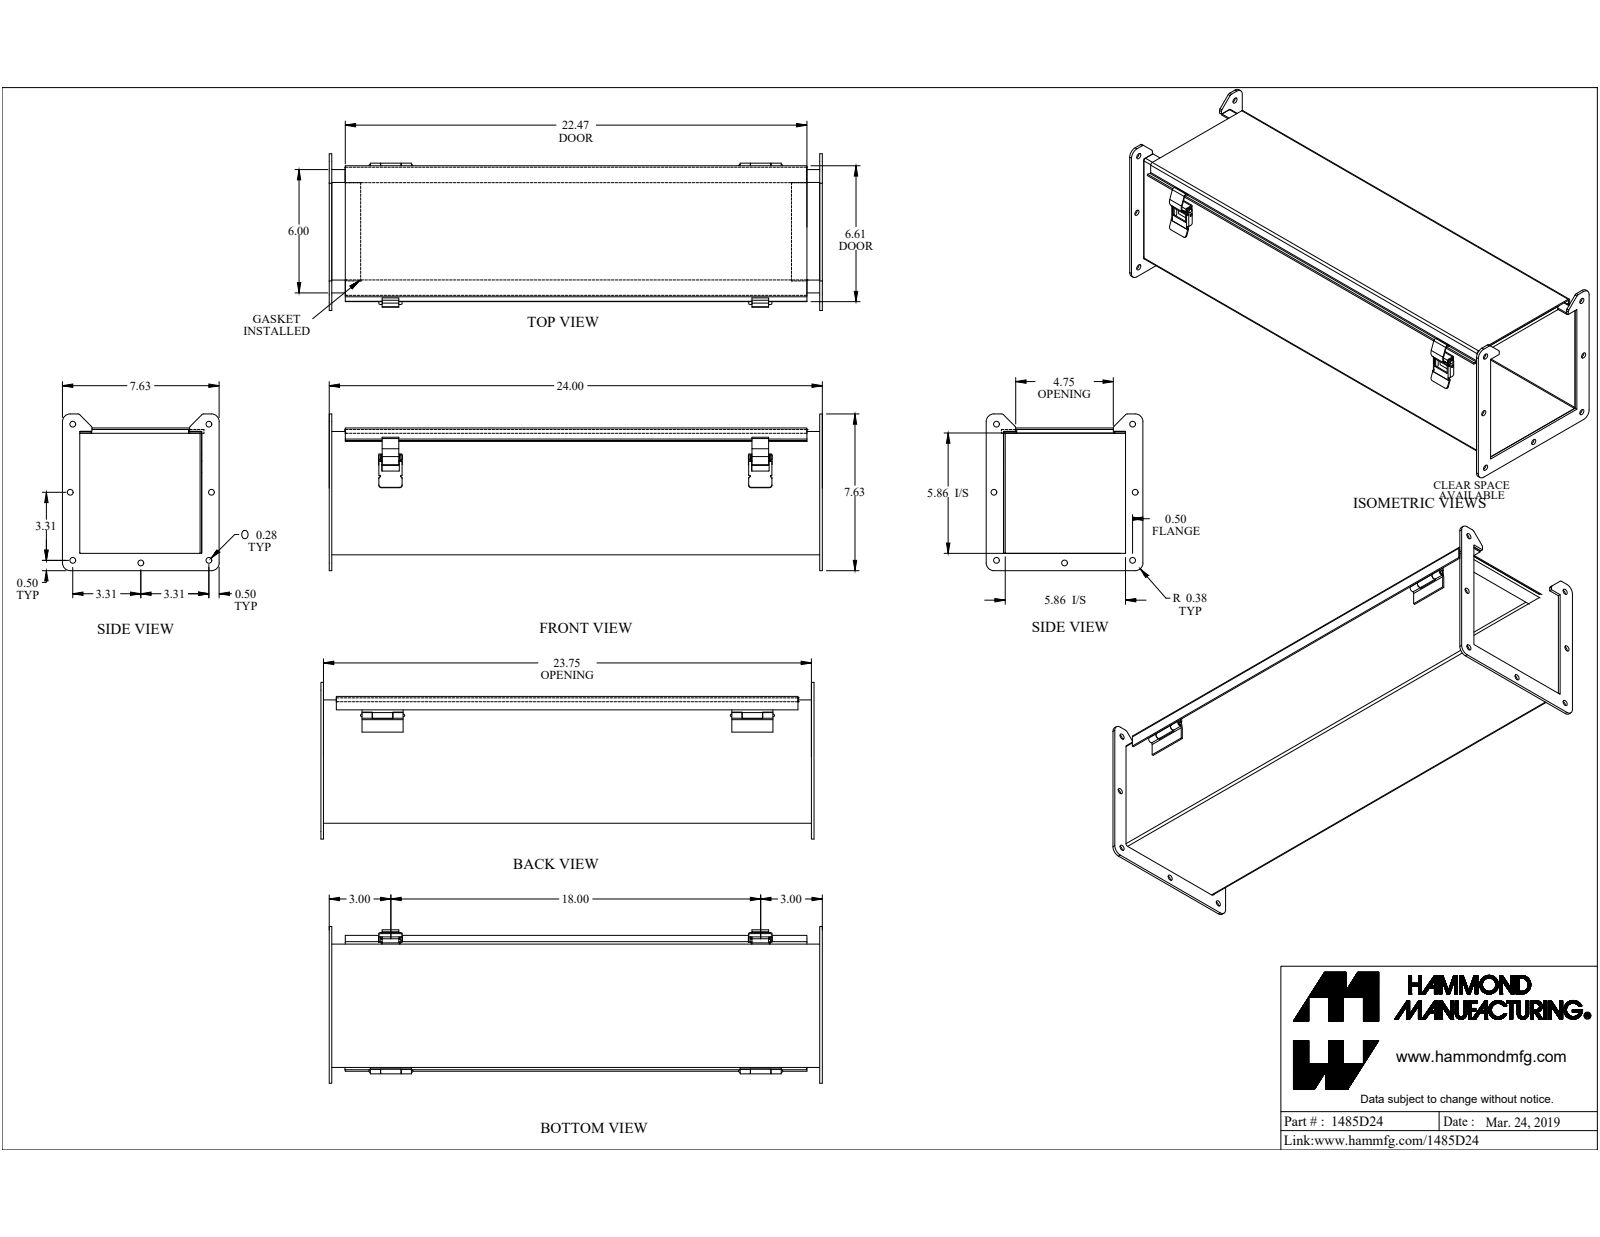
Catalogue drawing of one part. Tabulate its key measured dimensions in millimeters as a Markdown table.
| quantity | value |
| --- | --- |
| part name | 1485D24 |
| STEP written by | SolidWorks 2019 (CONFIG_CONTROL_DESIGN) |
| units | millimeters |
| bodies | 20 solids, 416 faces (250 planar, 162 cylindrical, 4 other) |
| overall size | 609.6 × 193.7 × 193.7 |
| volume | 949 000 mm³ |
| surface area | 953 500 mm² |
| round holes (diameter × count) | 7.1 × 7, 3.2 × 1, 3.3 × 1, 4.2 × 1 |
| round bosses / shafts (diameter × count) | 4.7 × 2, 7 × 1, 4 × 1, 3.2 × 1, 3.2 × 1 |
| partial cylindrical surfaces (radius × count) | 0.4 × 13, 3.2 × 9, 0.9 × 7, 2.7 × 7, 0.9 × 5, 1 × 5, 1.9 × 5, 0.4 × 4 |
| main face-to-face distances | 1.8, 150.6, 154.9, 152.4, 148.7, 153.1, 156.8, 4.4, 150.2, 148.4 |
| hole center spacings | 191, 168.3, 84.2, 84.2, 238, 7.2, 28.2, 37.1 |
